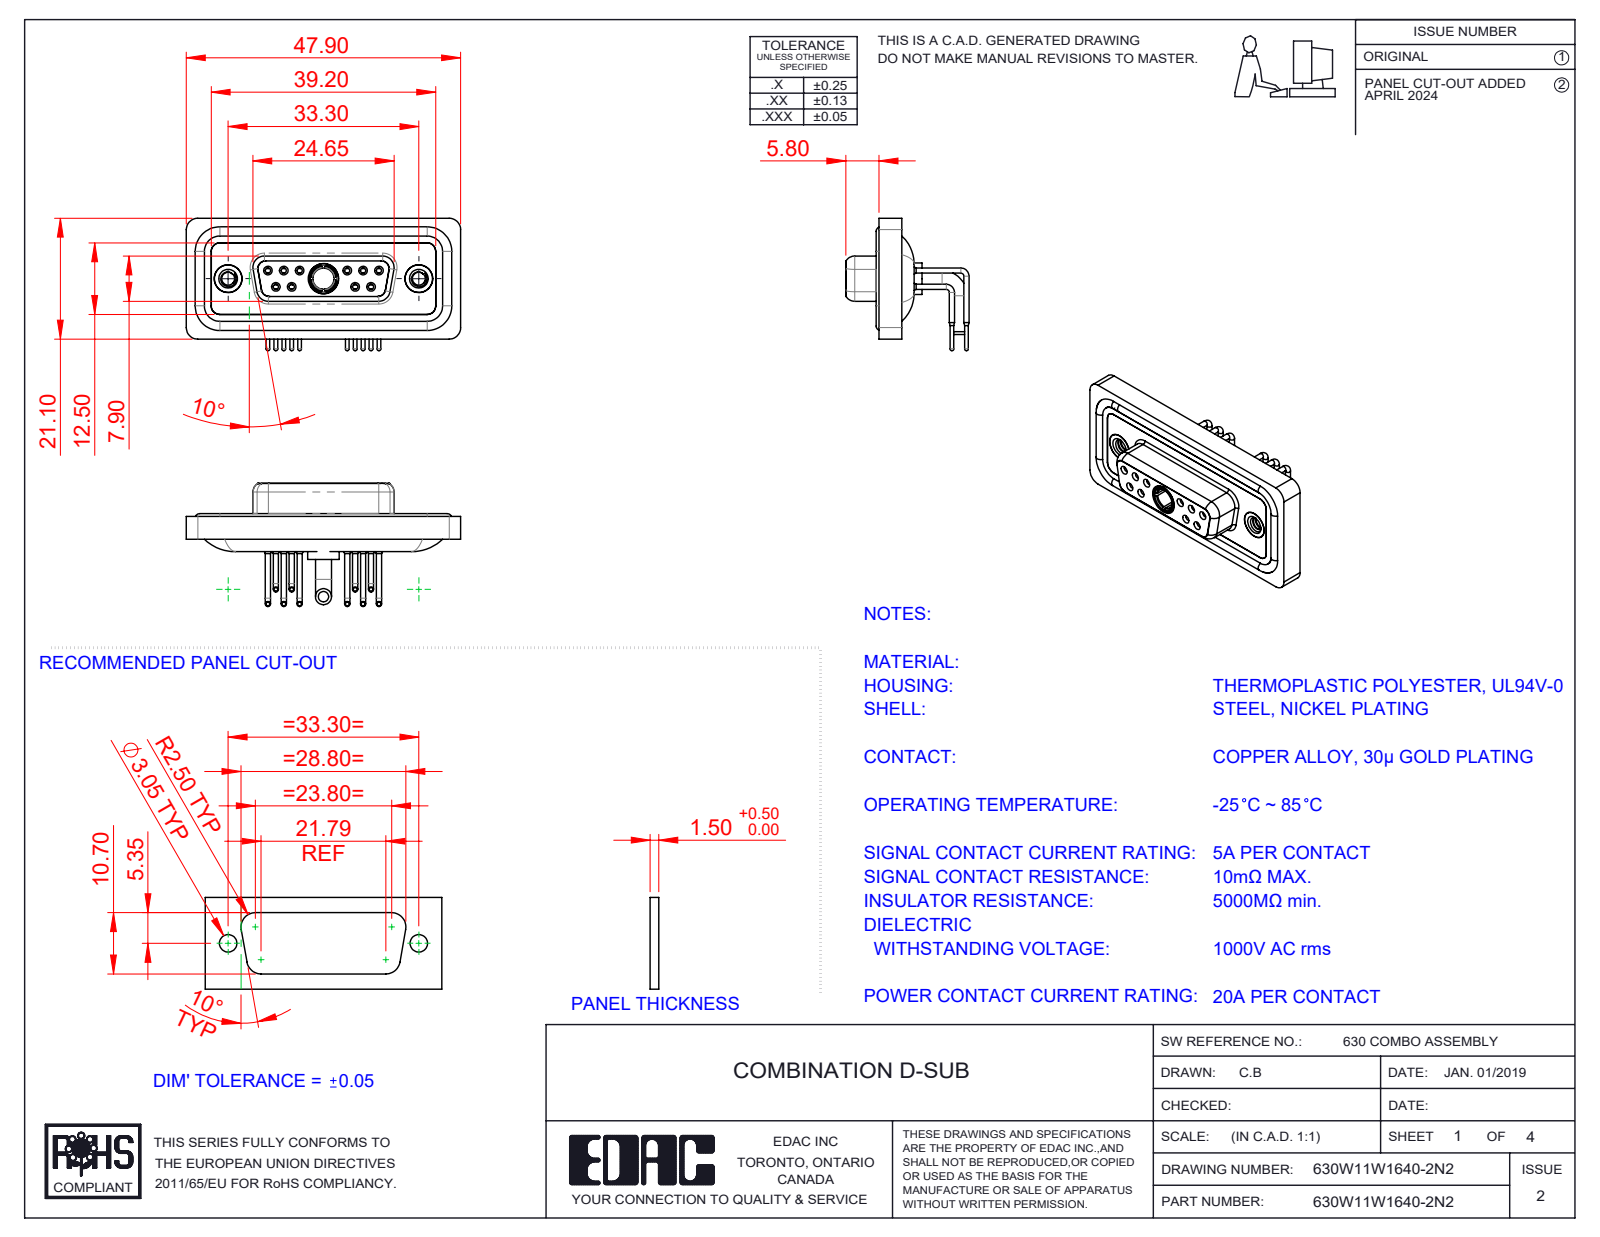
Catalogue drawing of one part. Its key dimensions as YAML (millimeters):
part_name: "Power Socket_20A RA; 630Combo Contact Row 2_50 Contacts; 630Combo Shell Front_15 Contacts; 630W11W1640-2N2 (+5 more)"
step_written_by: "SolidWorks 2023 (CONFIG_CONTROL_DESIGN)"
units: millimeters
bodies: {solids: 19, faces: 994, planar: 284, cylindrical: 443, other: 267}
overall_size: [47.9, 23.12, 21.53]
volume: 6217
surface_area: 10471
round_holes:
  - {diameter: 0.9, count: 10}
  - {diameter: 1.1, count: 10}
  - {diameter: 1.5, count: 10}
  - {diameter: 2, count: 10}
  - {diameter: 1.7, count: 6}
  - {diameter: 1.6, count: 4}
  - {diameter: 4.85, count: 3}
  - {diameter: 2.26, count: 2}
  - {diameter: 4, count: 2}
  - {diameter: 4.05, count: 2}
  - {diameter: 5, count: 2}
  - {diameter: 3.7, count: 1}
round_bosses_or_shafts:
  - {diameter: 1.6, count: 10}
  - {diameter: 0.9, count: 10}
  - {diameter: 0.65, count: 10}
  - {diameter: 4.95, count: 2}
  - {diameter: 4.8, count: 2}
  - {diameter: 2.8, count: 2}
  - {diameter: 5.5, count: 1}
  - {diameter: 5.2, count: 1}
partial_cylinders:
  - {radius: 2, count: 20}
  - {radius: 1.5, count: 18}
  - {radius: 1.35, count: 12}
  - {radius: 1.6, count: 8}
  - {radius: 0.25, count: 4}
  - {radius: 0.5, count: 4}
  - {radius: 0.6, count: 4}
  - {radius: 0.65, count: 4}
face_to_face_distances: [0.4, 1.8, 1.1, 1.6, 2.5, 2.9, 3.1, 3.7, 4.1, 1.5]
hole_center_spacings: [3.16, 2.77, 13.85, 11.08, 16.62, 5.03, 5.04, 5.54]
